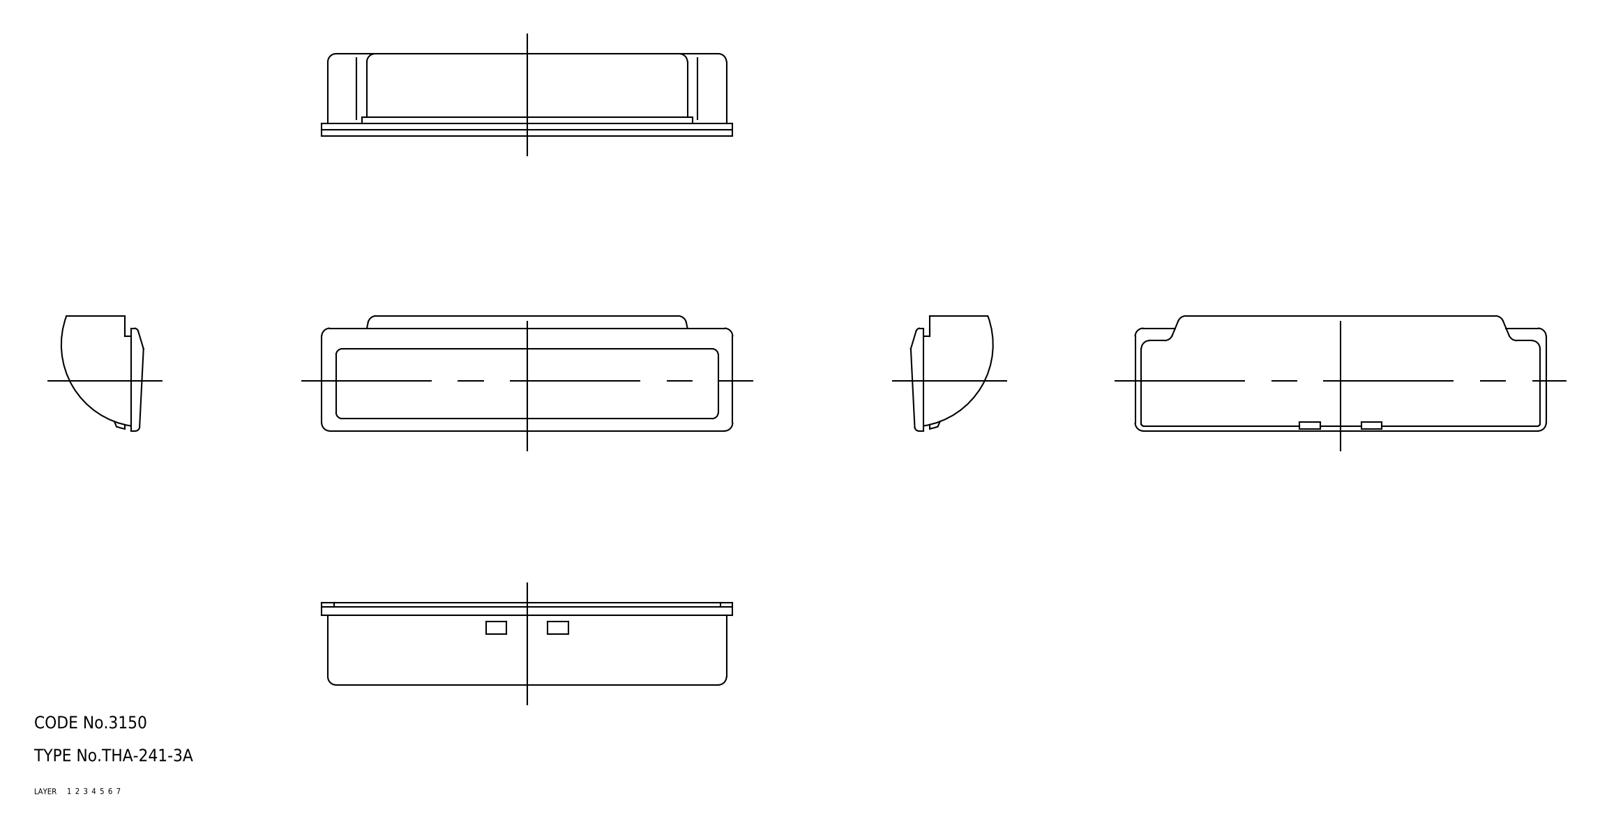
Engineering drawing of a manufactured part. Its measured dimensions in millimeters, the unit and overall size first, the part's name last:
Units: millimetres
Overall size (bounding box): 100 × 28 × 19.99
Volume: 12 343 mm³ · Surface area: 13 016 mm²
Bodies: 1 solid, 88 faces (0 planar, 0 cylindrical, 88 other)
Part name (STEP PRODUCT): 67113819
STEP written by: CADfix (AUTOMOTIVE_DESIGN)
